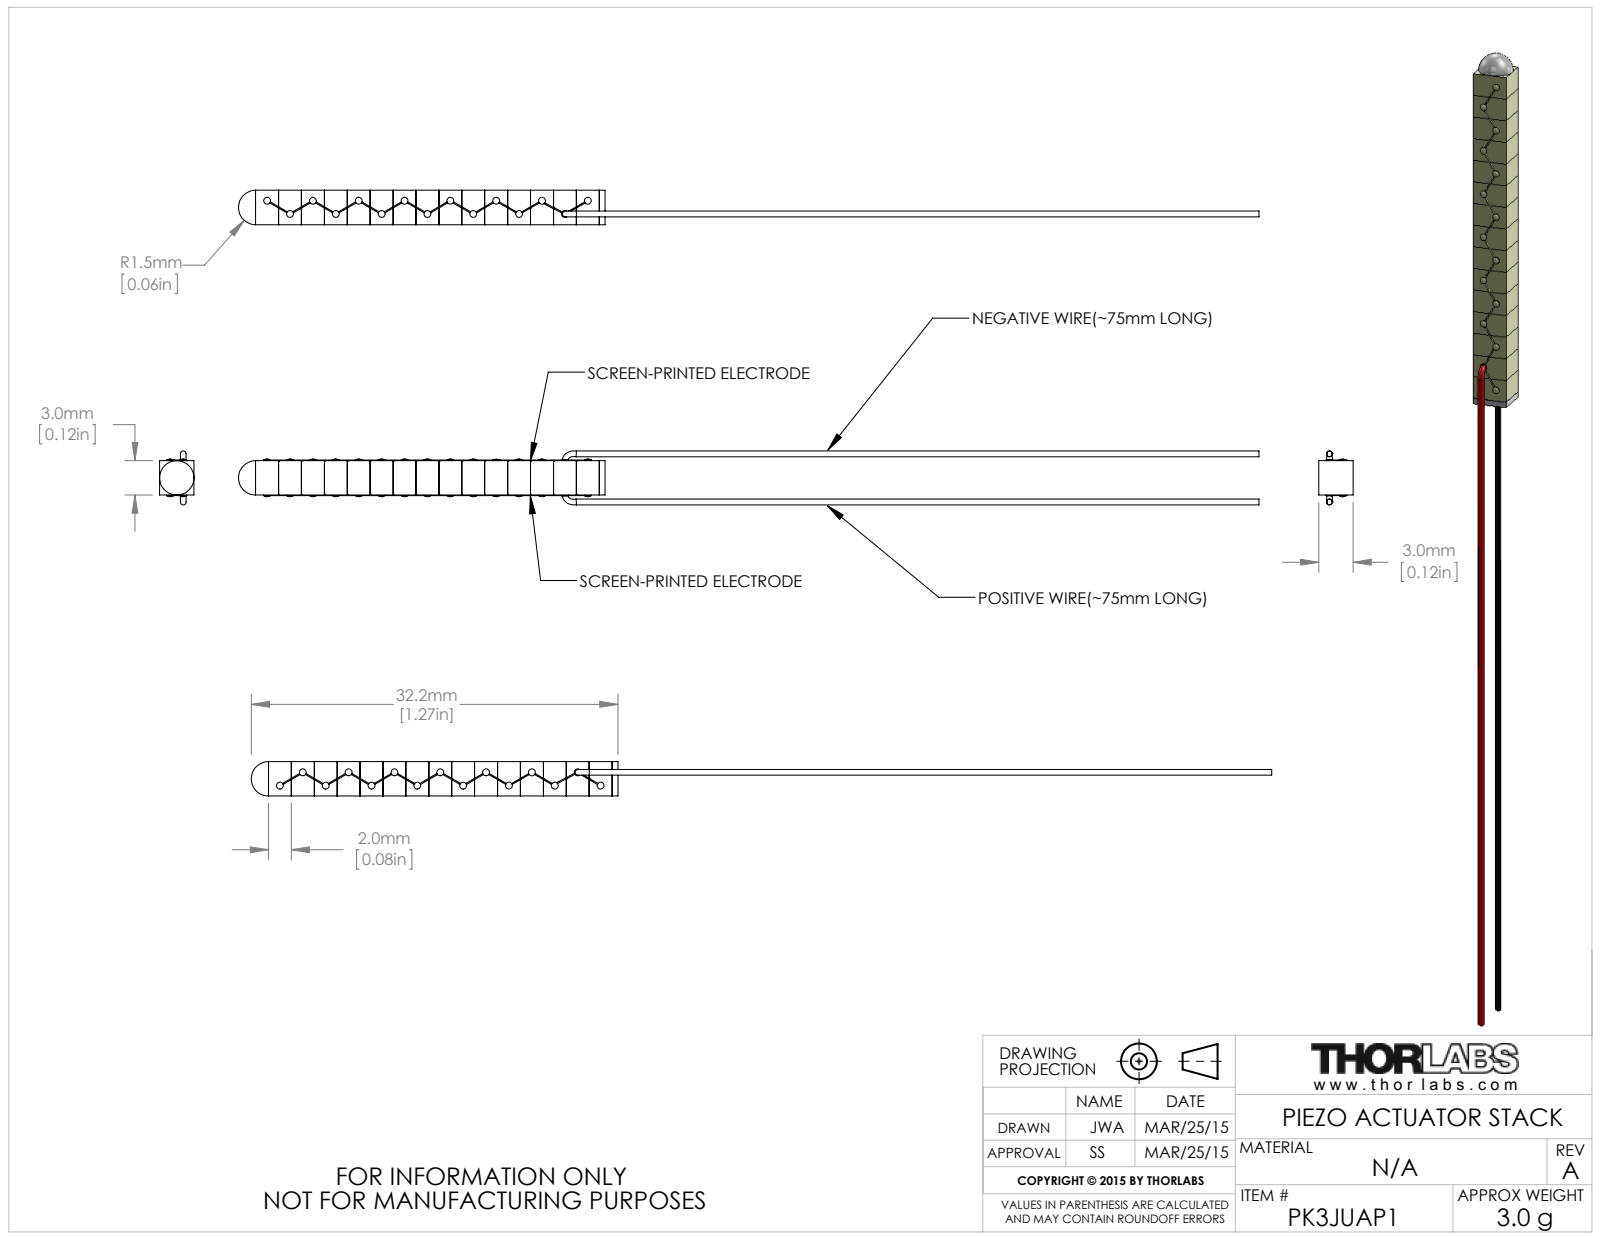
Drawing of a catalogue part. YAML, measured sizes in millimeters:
part_name: "CTN002742"
step_written_by: "SolidWorks 2014 (AUTOMOTIVE_DESIGN)"
units: millimeters
bodies: {solids: 19, faces: 312, planar: 118, cylindrical: 126, other: 68}
overall_size: [89.1, 4.72, 3]
volume: 307
surface_area: 876
round_bosses_or_shafts:
  - {diameter: 0.6, count: 15}
face_to_face_distances: [2, 4, 6, 8, 3, 10, 12, 14, 16, 18]
